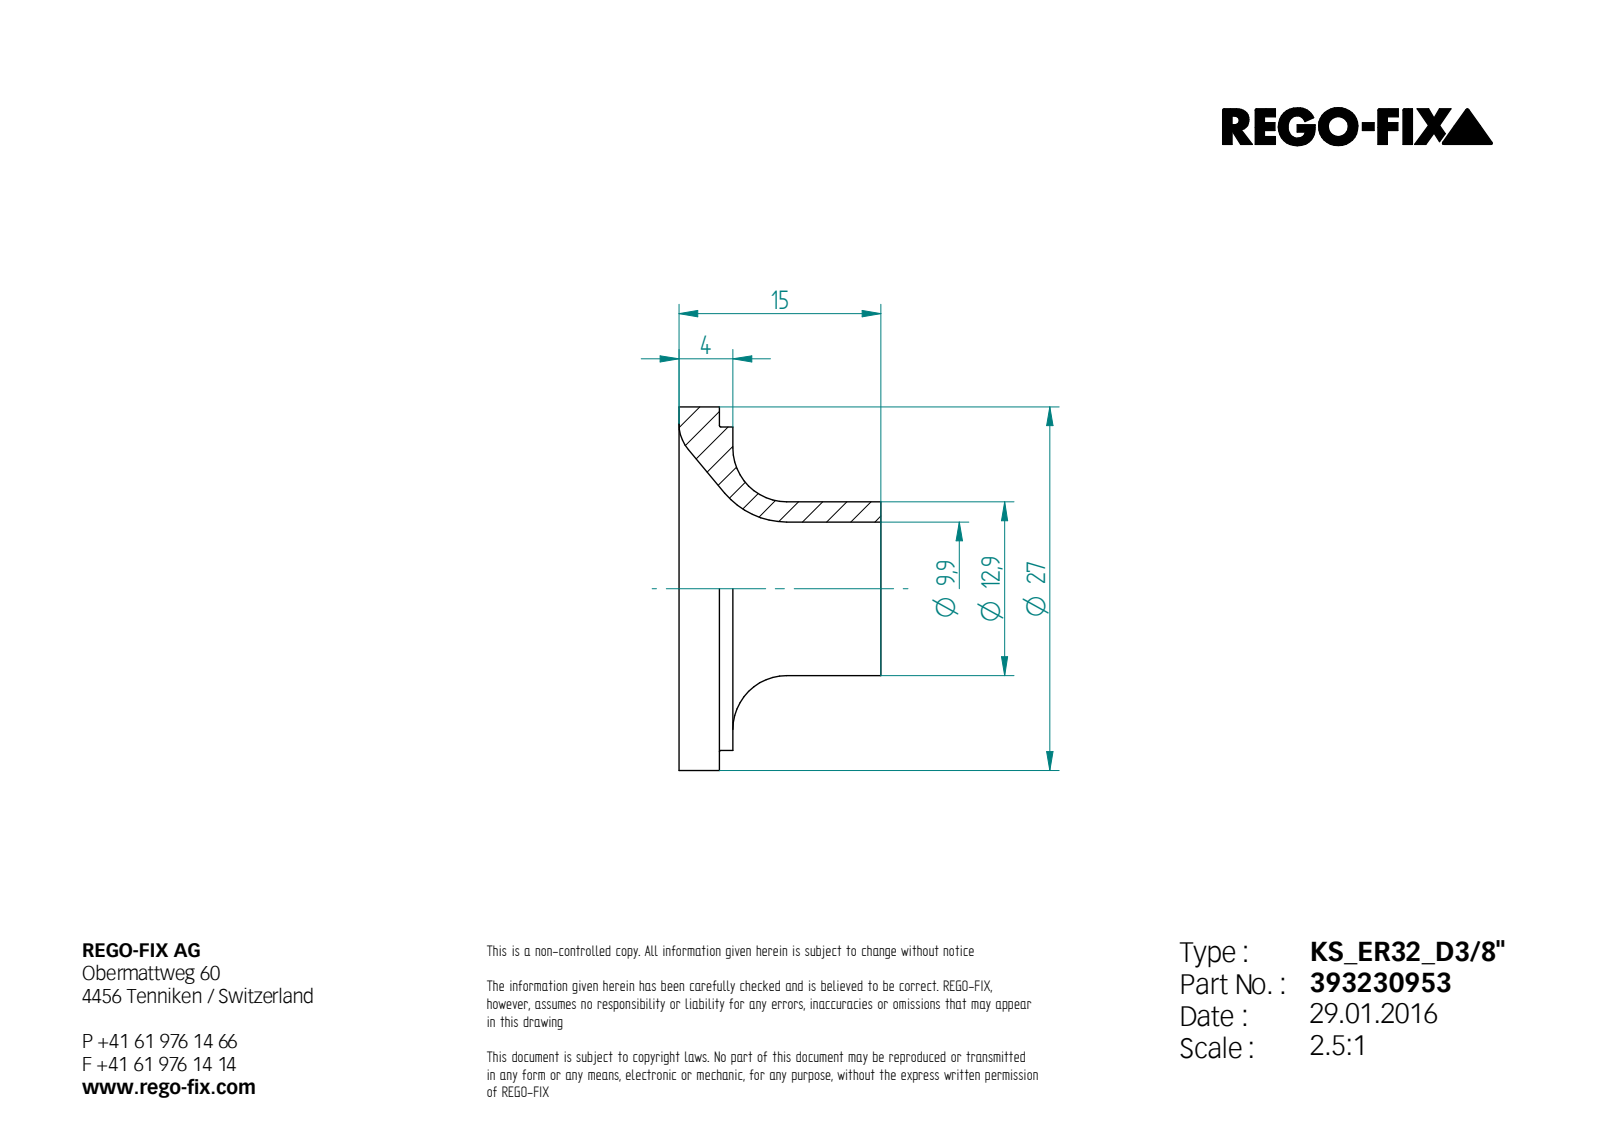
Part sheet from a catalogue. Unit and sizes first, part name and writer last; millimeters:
Units: millimetres
Overall size (bounding box): 27 × 27 × 15
Round holes (diameter × count): ⌀9.9 ×1
Round bosses / shafts (diameter × count): ⌀27 ×1, ⌀24 ×1, ⌀12.9 ×1
Main face-to-face distances: 1, 3, 4, 15, 12, 11
Volume: 1 854 mm³ · Surface area: 2 090 mm²
Bodies: 1 solid, 13 faces (4 planar, 4 cylindrical, 5 other)
STEP written by: Unknown (AUTOMOTIVE_DESIGN)
